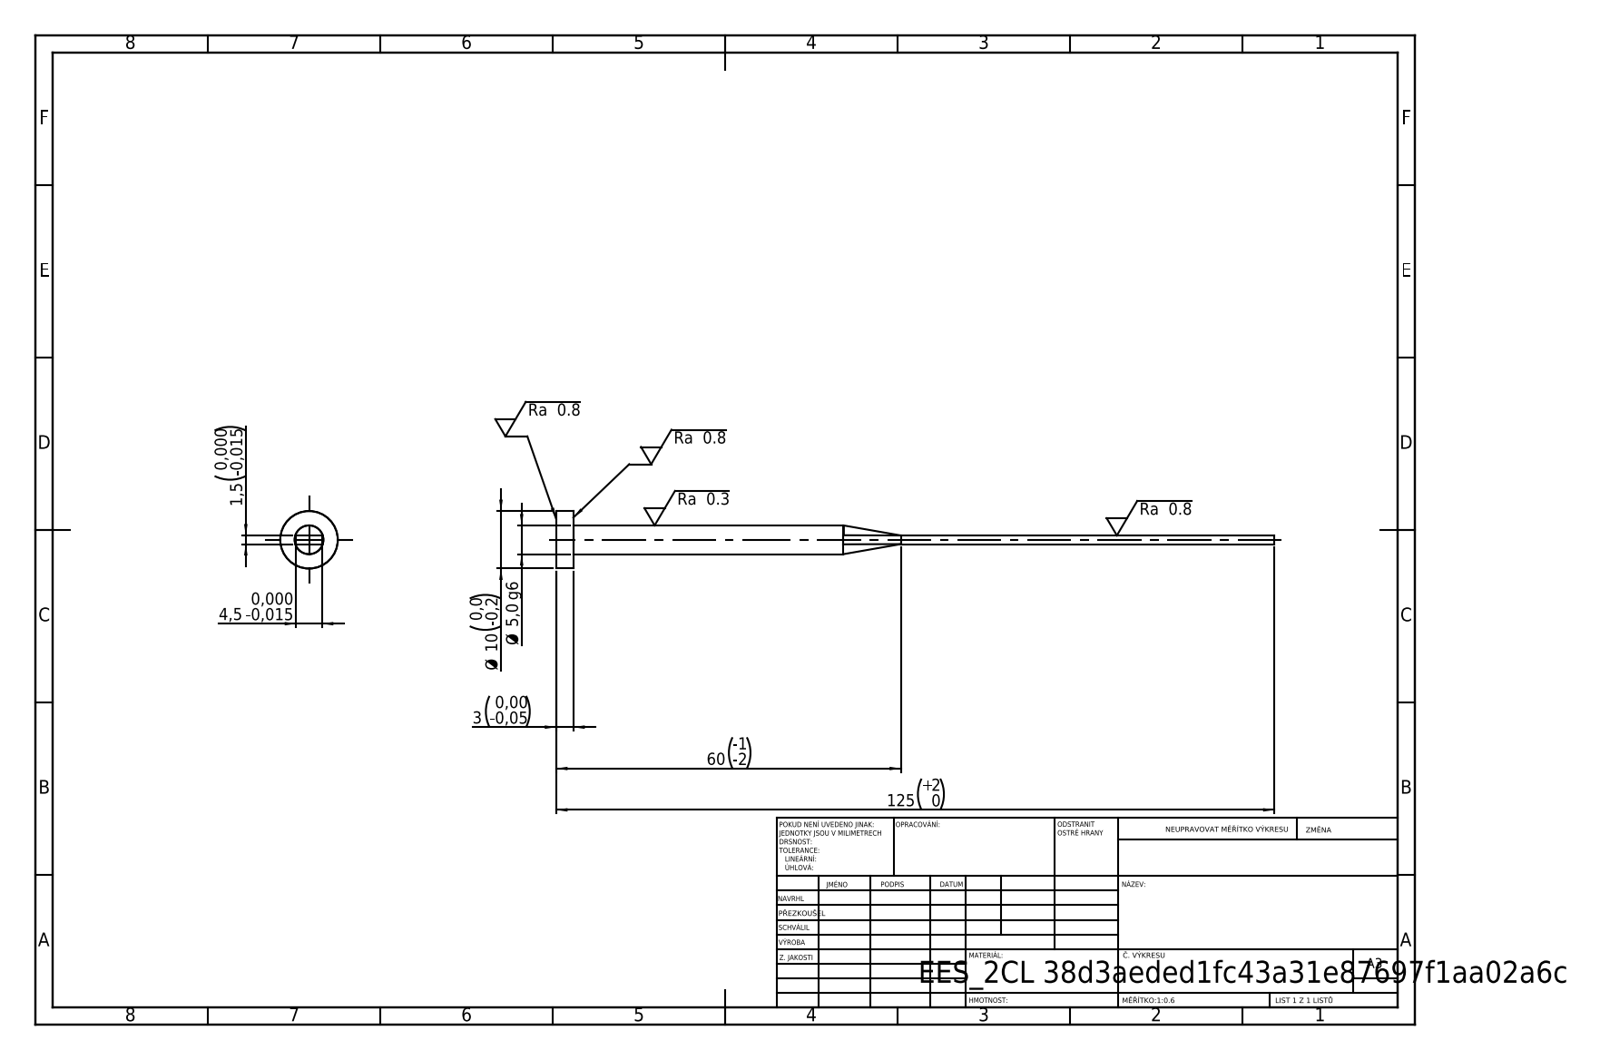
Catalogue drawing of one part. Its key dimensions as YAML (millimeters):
step_written_by: "SolidWorks 2019 (CONFIG_CONTROL_DESIGN)"
units: millimeters
bodies: {solids: 1, faces: 15, planar: 7, cylindrical: 4, other: 4}
overall_size: [125, 10, 10]
volume: 1725
surface_area: 1891
round_bosses_or_shafts:
  - {diameter: 10, count: 1}
  - {diameter: 5, count: 1}
face_to_face_distances: [1.5, 4.5, 3, 125, 122]
